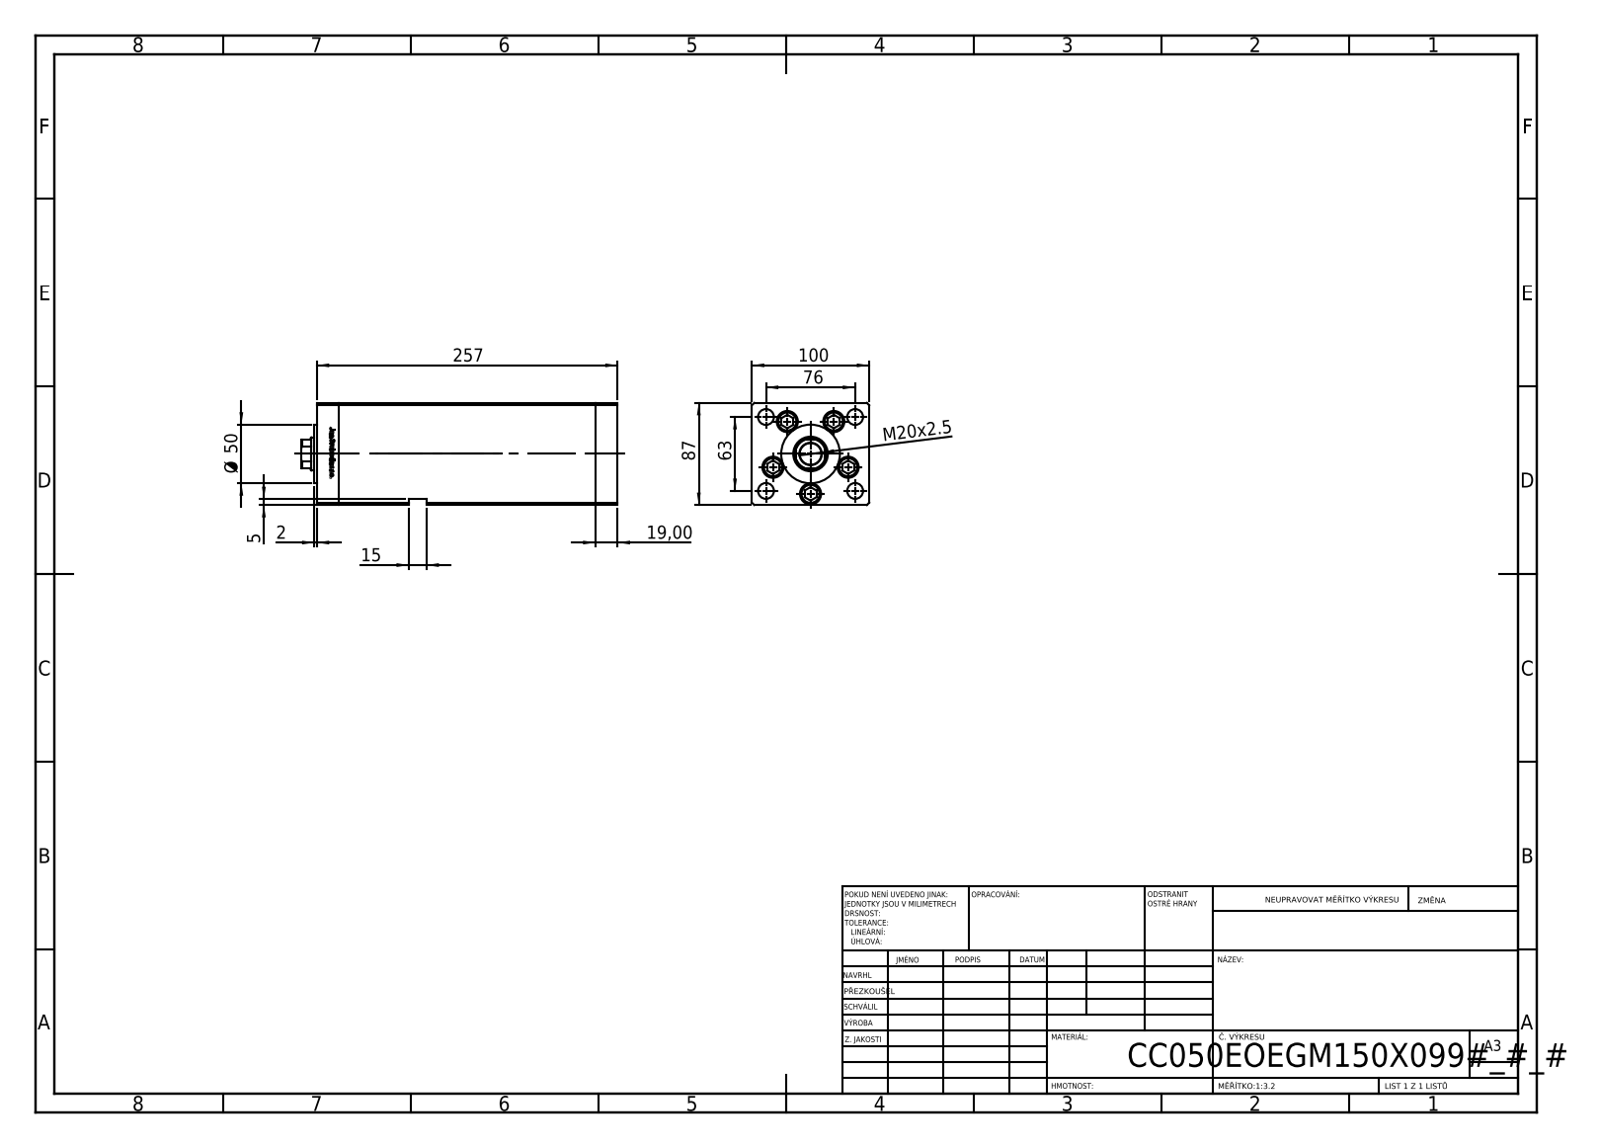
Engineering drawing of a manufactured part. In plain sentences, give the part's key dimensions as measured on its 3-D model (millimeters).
The part is named "V220C BACK_E; V220C_FRONT_E; V220C_E MIDDLE; ALLEN BOLT (+1 more)". Its 3-D file was written by "SolidWorks 2019 (CONFIG_CONTROL_DESIGN)". It is 14 solids with 1214 faces: 475 planar, 165 cylindrical and 574 other. Overall it measures 269.5 by 100 by 87 millimeters. Its volume is 1 865 000 cubic millimeters and its surface area 265 778 square millimeters. Round holes: 11 of diameter 13.5, 5 of diameter 18, 5 of diameter 18.5, 4 of diameter 12.5, 2 of diameter 2, 2 of diameter 13.16, 1 of diameter 28, 1 of diameter 29.5. Round bosses or shafts: 5 of diameter 17, 5 of diameter 8, 1 of diameter 50. Partial cylindrical surfaces (rounded edges, fillets, slot ends): 2 of radius 0.93, 1 of radius 13.5. The main face-to-face distances are 100, 87, 19, 218.5, 237.5, 34.25, 256.5, 15.25, 203.25, 222.25. The hole center spacings are 34, 18.59, 39.64, 49.36, 57.95, 21.03, 38.08, 39.27.
